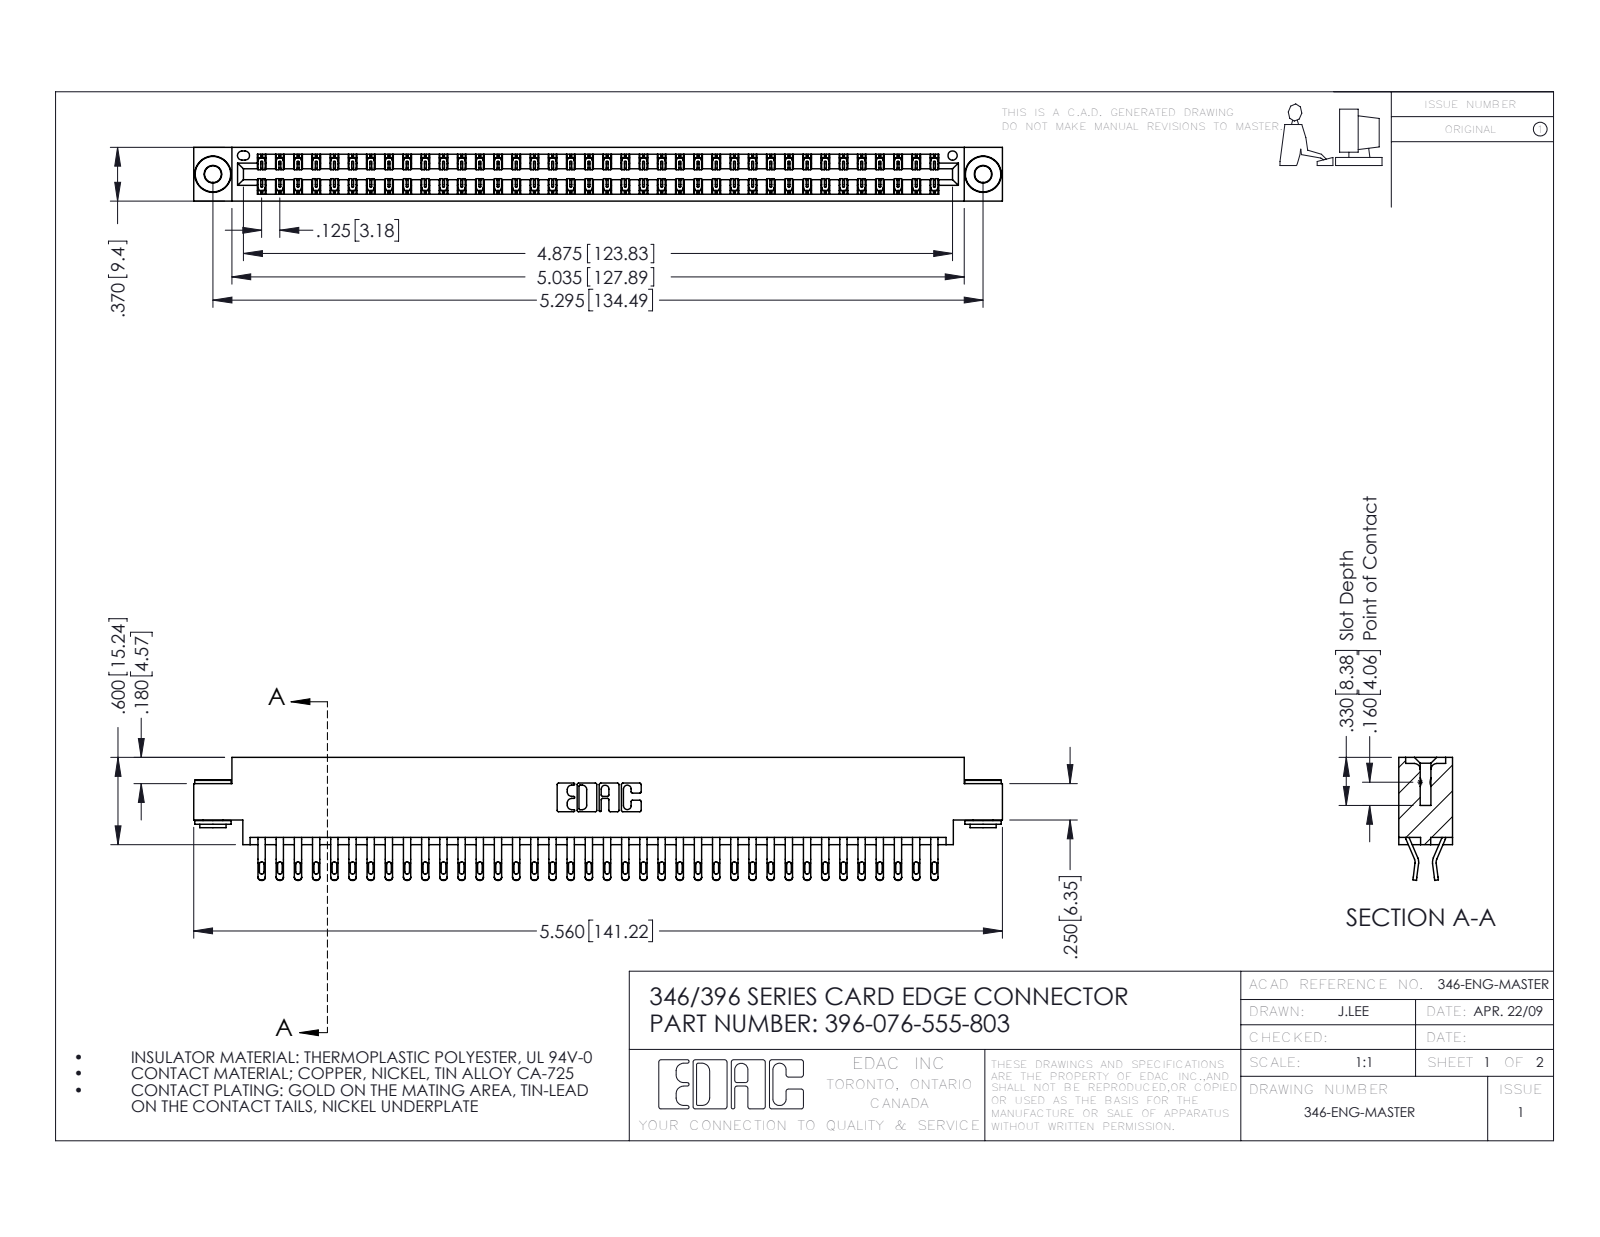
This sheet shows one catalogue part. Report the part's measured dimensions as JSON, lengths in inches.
{"part_name": "396-076-555-803; 345-250-002_345-250-002-102; 346 Part_0.170 Offset - 0.156 Dia-TH; 345-292-001_555 Tail", "step_written_by": "SolidWorks 2016 (CONFIG_CONTROL_DESIGN)", "units": "inches", "bodies": {"solids": 79, "faces": 4572, "planar": 2598, "cylindrical": 1966, "other": 8}, "overall_size": [5.56, 0.845, 0.37], "volume_in3": 0.844, "surface_area_in2": 31.19, "round_holes": [[0.116, 2], [0.156, 2], [0.064, 1]], "round_bosses_or_shafts": [[0.25, 2], [0.18, 2], [0.136, 2]], "partial_cylinders_radius": [[0.016, 152], [0.02, 152], [0.006, 114], [0.01, 22], [0.007, 6], [0.031, 6], [0.026, 3], [0.01, 2]], "face_to_face_distances": [0.048, 0.322, 0.37, 0.25, 0.025, 0.275, 0.072, 0.298, 0.148, 0.222], "hole_center_spacings": [0.246, 5.086, 5.295]}
